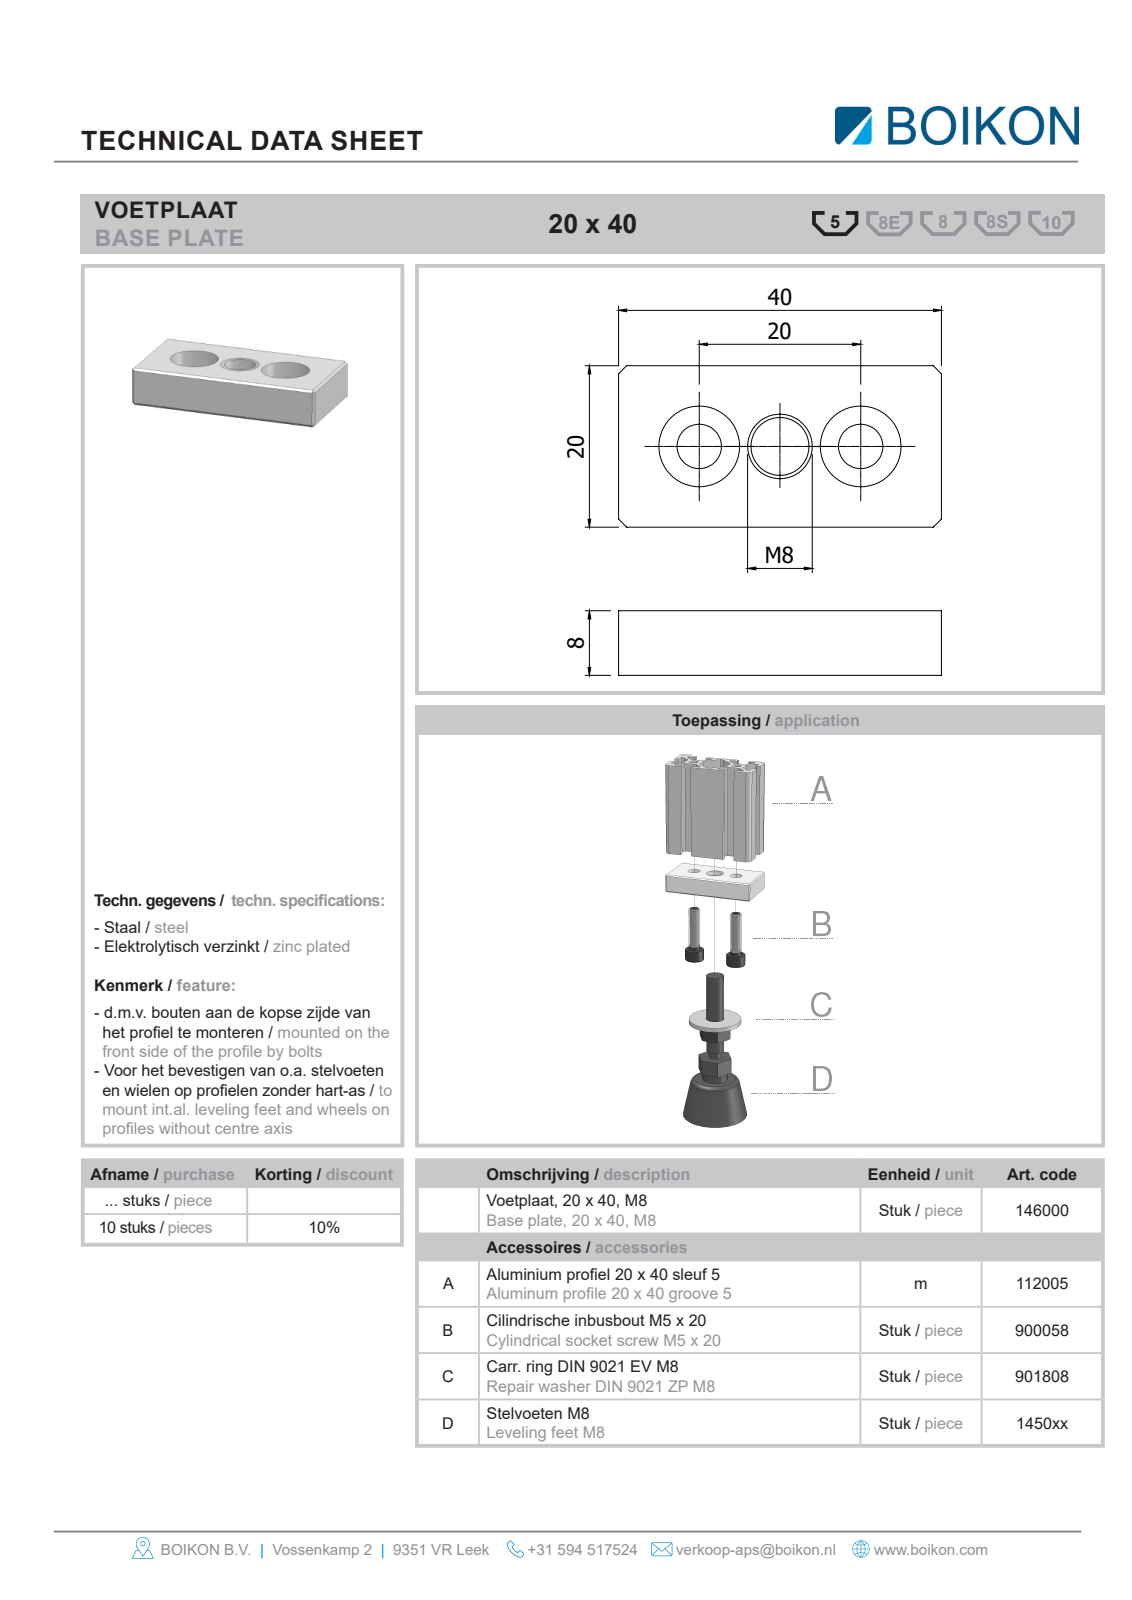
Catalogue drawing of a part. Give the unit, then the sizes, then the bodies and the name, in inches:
Units: inches
Overall size (bounding box): 1.575 × 1 × 0.787
Round holes (diameter × count): ⌀0.217 ×2, ⌀0.394 ×2, ⌀0.315 ×1
Round bosses / shafts (diameter × count): ⌀0.335 ×2, ⌀0.197 ×2, ⌀0.158 ×2
Main face-to-face distances: 0.315, 0.787, 0.102, 0.213, 1.575, 0.299, 0.197, 0.016, 0.157, 0.685
Hole centre spacings: 0.394, 0.787
Volume: 0.369 in³ · Surface area: 6.288 in²
Bodies: 3 solids, 55 faces (38 planar, 11 cylindrical, 6 other)
Part name (STEP PRODUCT): Root; 146000 - Voetplaat 20 x 40 M8 BOIKON; 900058Cil. inbusbout DIN 912 EV M5 x 20BOIKON0
STEP written by: HiCAD 2013 1802.4 Build 509 (AUTOMOTIVE_DESIGN)
